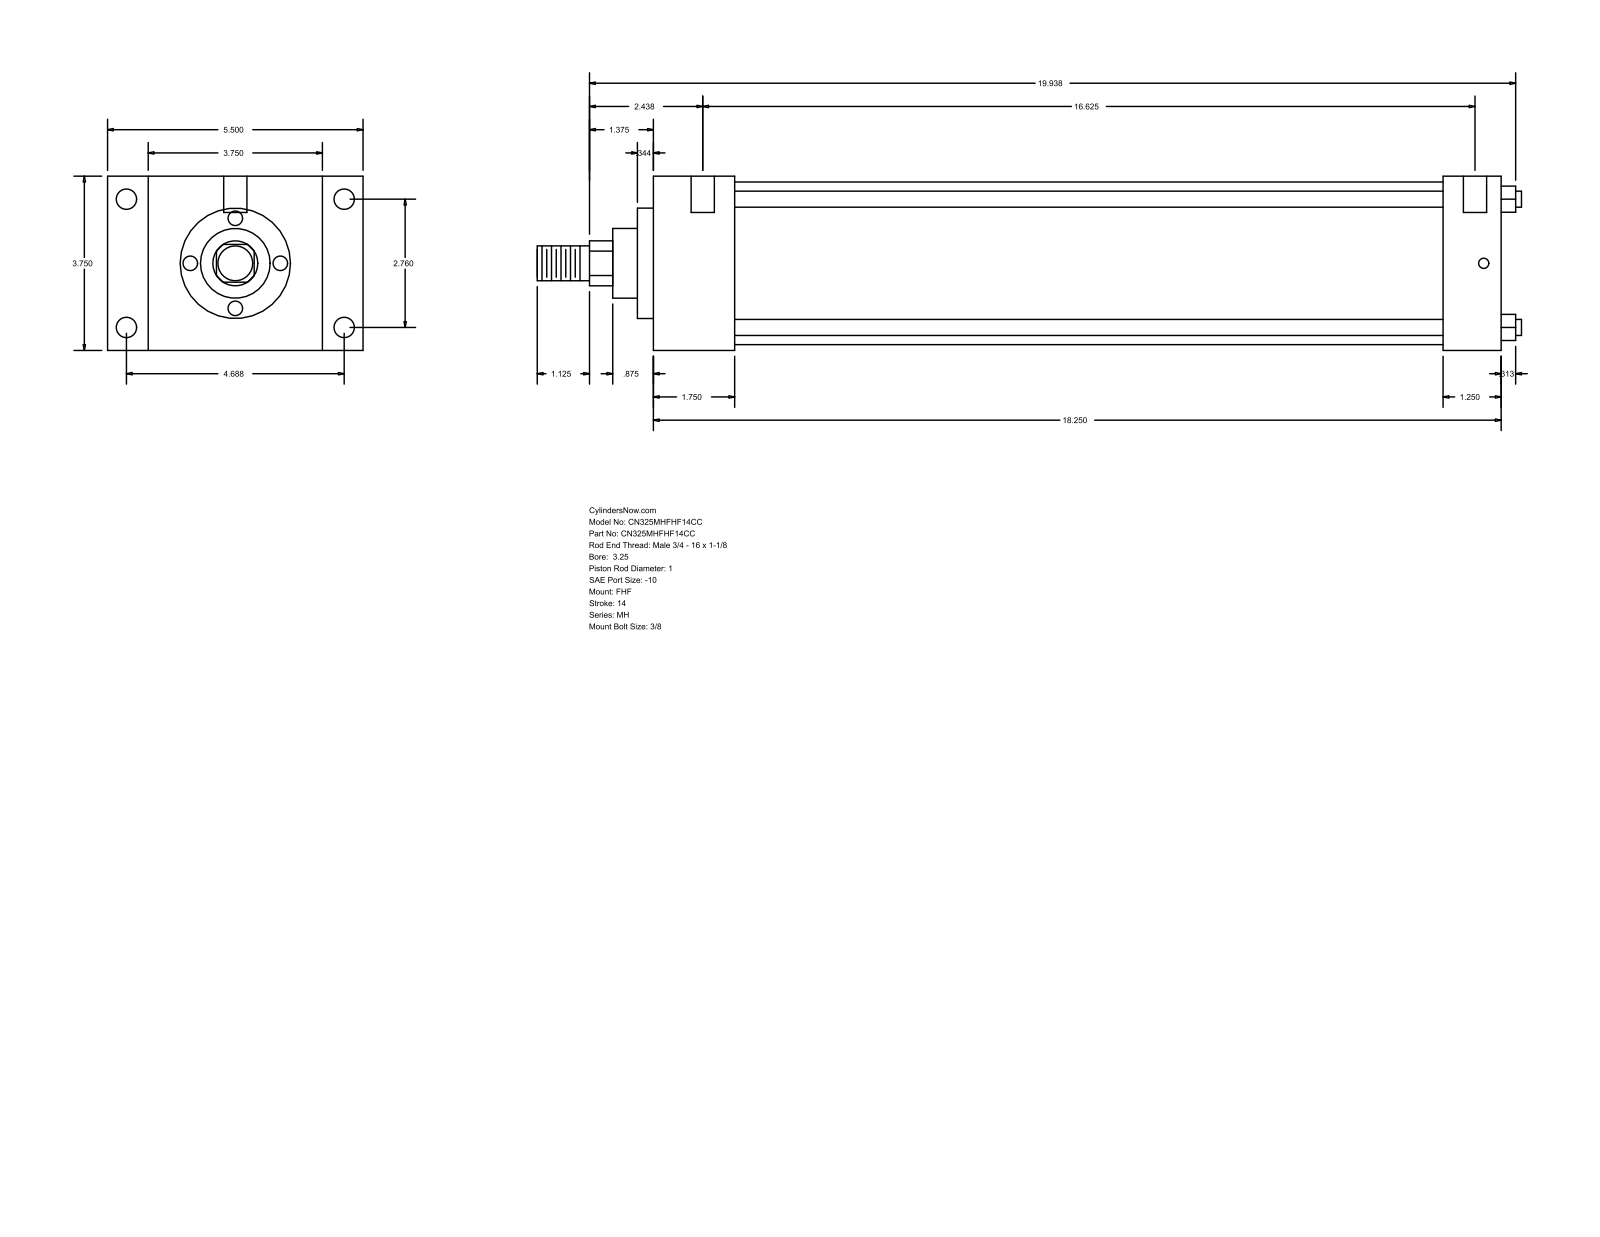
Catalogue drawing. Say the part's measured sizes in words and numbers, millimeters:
The part is named "MH_FHF__0325_1". Its 3-D file was written by "GSSL Pune (CONFIG_CONTROL_DESIGN)". It is 0 solids with 90 faces: 61 planar, 29 cylindrical and 0 other. Overall it measures 538.16 by 139.7 by 95.25 millimeters. Round holes: 4 of diameter 5.56, 4 of diameter 11.13, 2 of diameter 12.7. Round bosses or shafts: 4 of diameter 8.76, 1 of diameter 88.9, 1 of diameter 60.33, 1 of diameter 38.1, 1 of diameter 25.4, 1 of diameter 19.05. Partial cylindrical surfaces (rounded edges, fillets, slot ends): 1 of radius 12.29. The main face-to-face distances are 95.24, 463.56, 44.46, 419.1, 22.23, 117.47, 139.7, 431.81, 387.35, 31.75. The hole center spacings are 70.1, 119.06, 138.16, 428.62, 1.58, 4.76, 422.28, 423.86.
